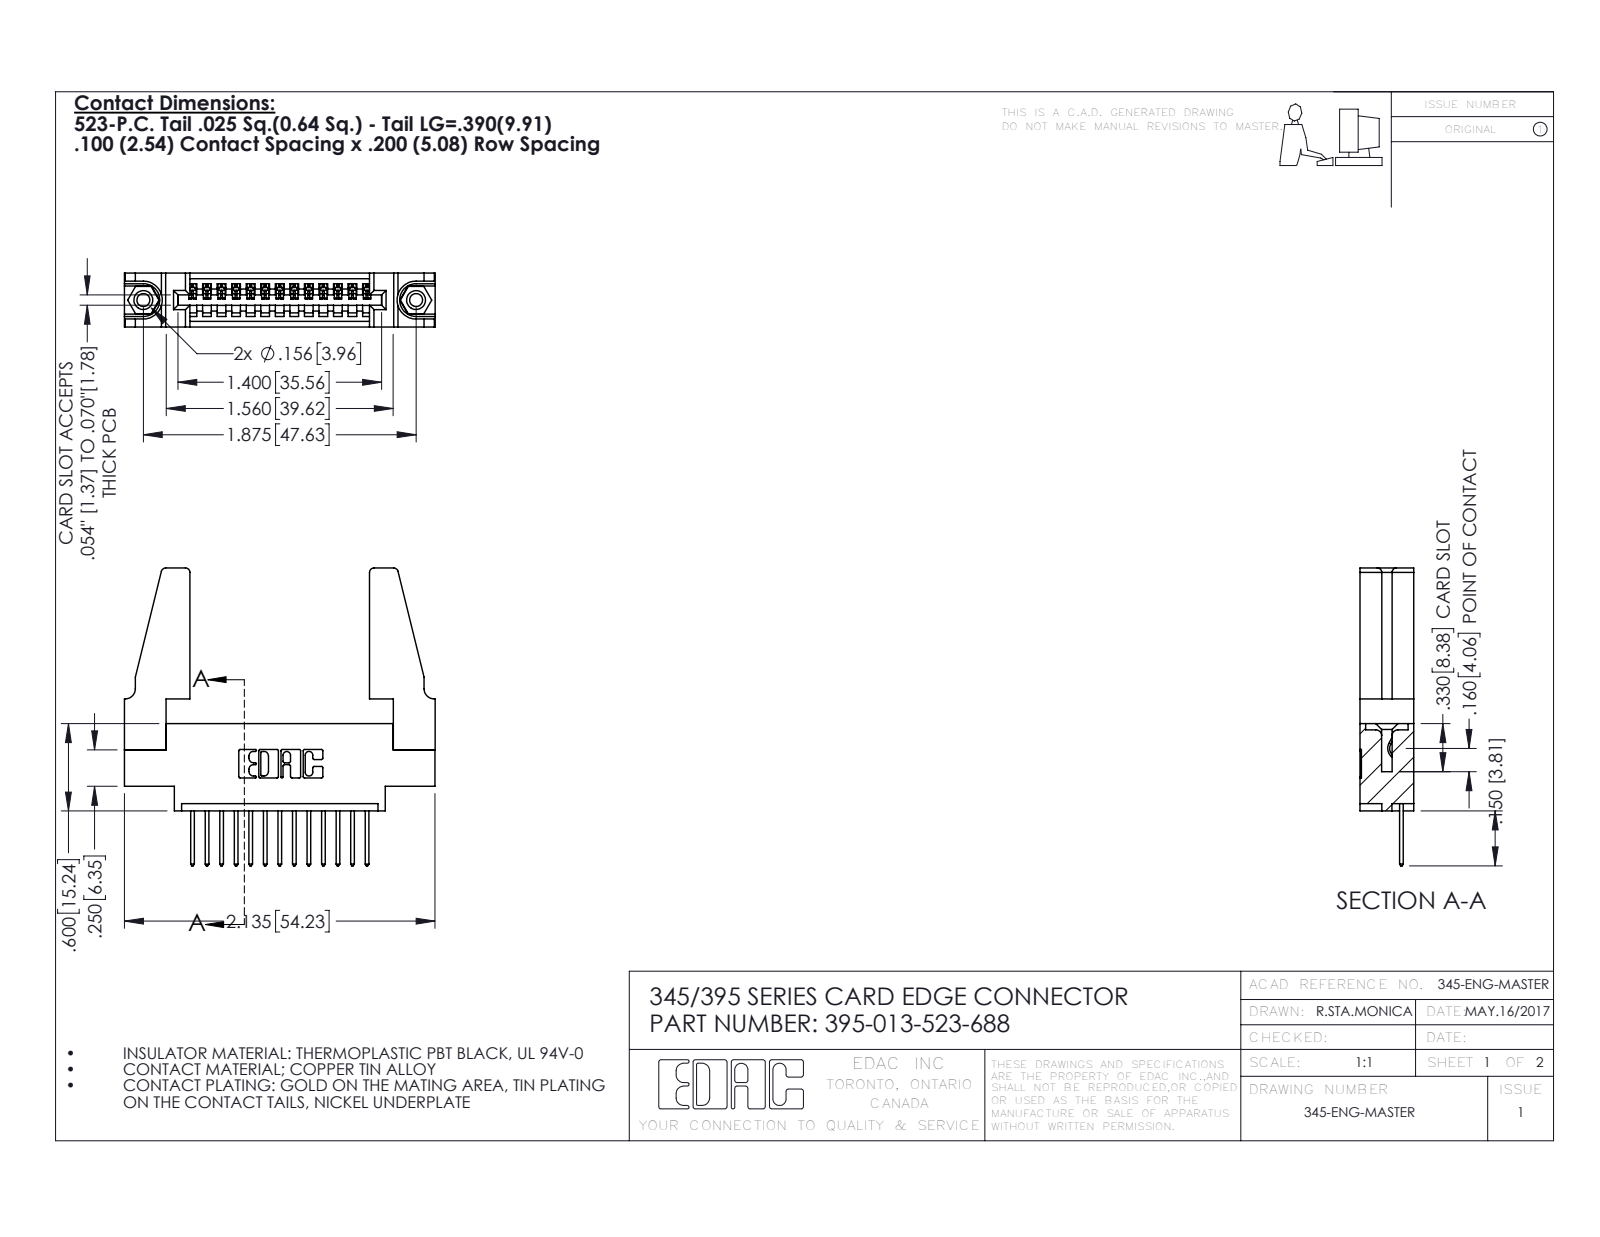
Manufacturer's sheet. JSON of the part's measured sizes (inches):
{"part_name": "345-220-078_345-220-088; 395-013-523-688; 345-250-001_345-250-001-102; 345 Part_0.170 Offset - 0.156 Dia-TH (+1 more)", "step_written_by": "SolidWorks 2016 (CONFIG_CONTROL_DESIGN)", "units": "inches", "bodies": {"solids": 18, "faces": 1008, "planar": 676, "cylindrical": 316, "other": 16}, "overall_size": [2.136, 2.047, 0.37], "volume_in3": 0.491, "surface_area_in2": 14.34, "round_holes": [[0.089, 2], [0.125, 2], [0.156, 2], [0.064, 1]], "round_bosses_or_shafts": [[0.155, 2]], "partial_cylinders_radius": [[0.006, 26], [0.01, 26], [0.01, 22], [0.03, 8], [0.007, 6], [0.031, 6], [0.026, 3], [0.031, 2]], "face_to_face_distances": [0.37, 0.072, 0.298, 0.2, 0.098, 0.272, 0.025, 0.225, 0.148, 0.15], "hole_center_spacings": [0.27, 1.643, 1.875]}
